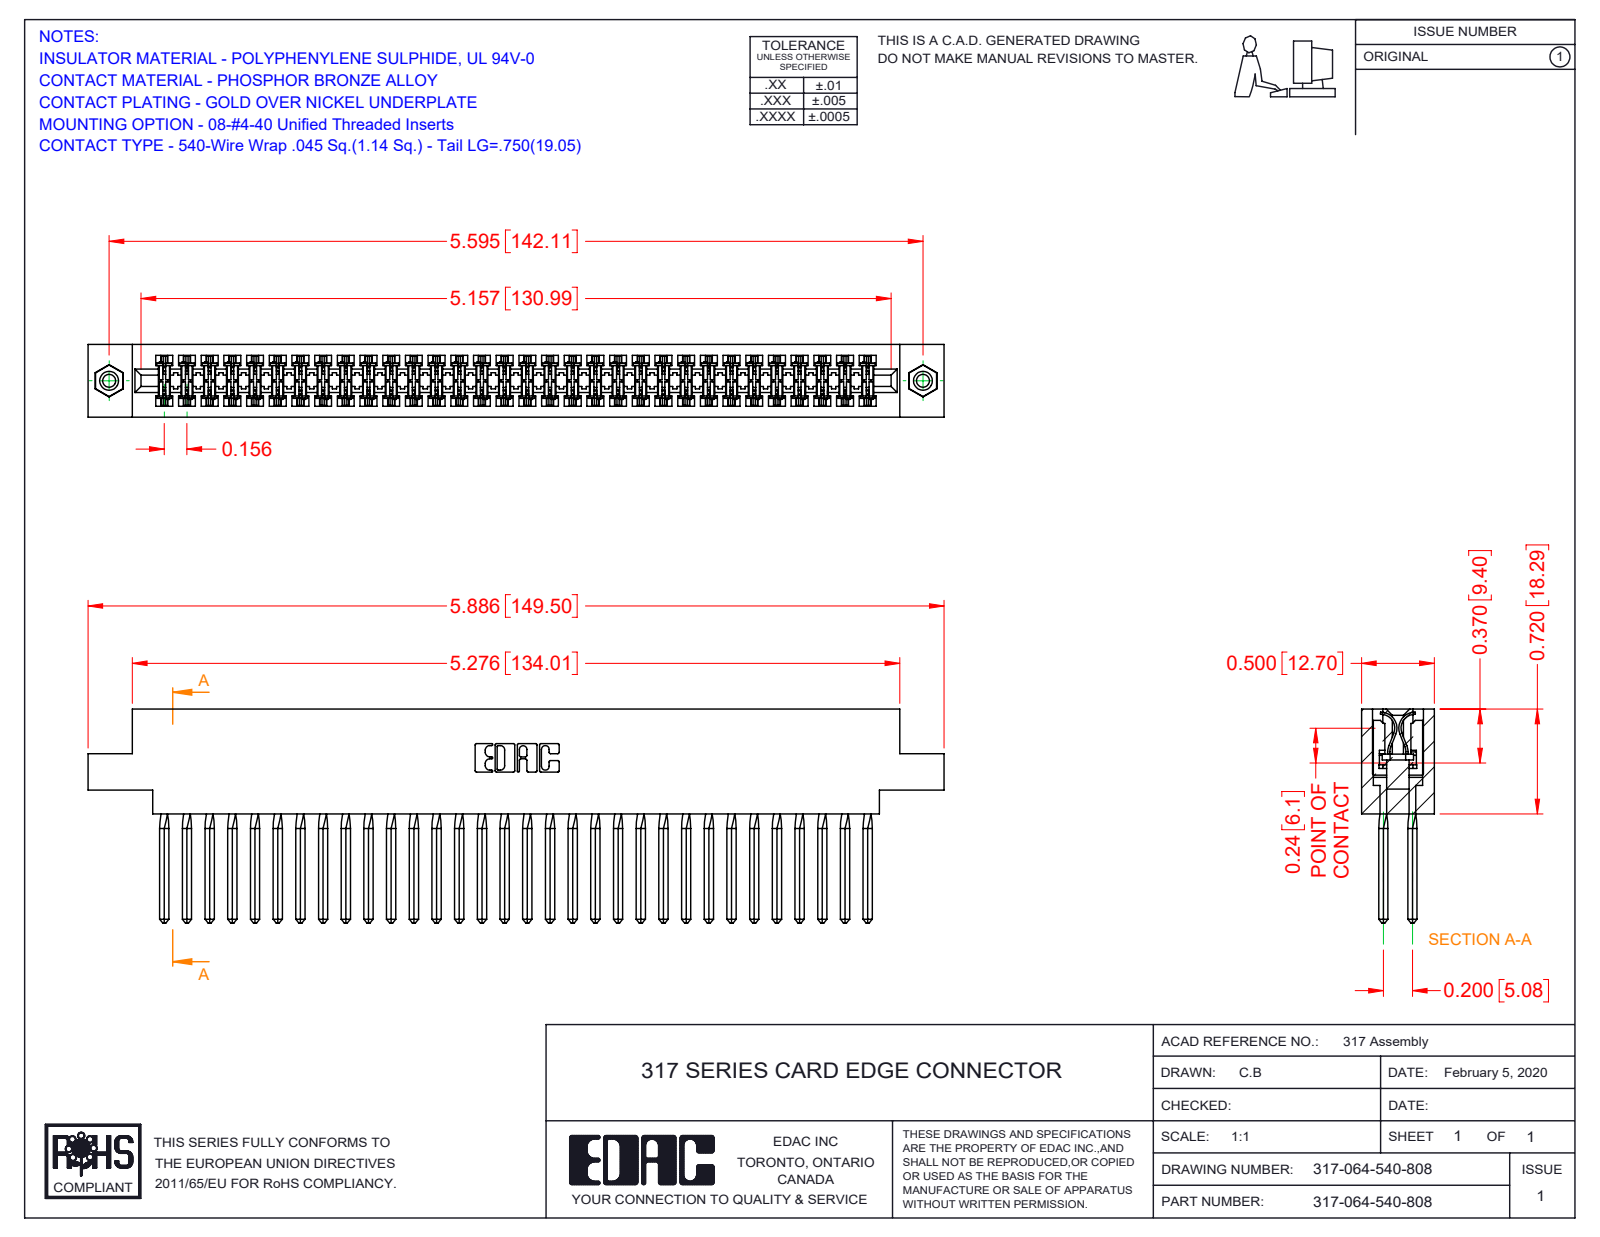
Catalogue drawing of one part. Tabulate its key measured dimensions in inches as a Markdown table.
| quantity | value |
| --- | --- |
| part name | 317-064-540-808; 317 Part_.156 Dia - TI; 317-290-001_540; 345-250-001_345-250-003-102 |
| STEP written by | SolidWorks 2016 (CONFIG_CONTROL_DESIGN) |
| units | inches |
| bodies | 67 solids, 5858 faces (4762 planar, 824 cylindrical, 272 other) |
| overall size | 5.886 × 1.47 × 0.5 |
| volume | 1.51 in³ |
| surface area | 56.64 in² |
| round holes (diameter × count) | 0.089 × 2, 0.125 × 2, 0.156 × 2 |
| round bosses / shafts (diameter × count) | 0.155 × 2 |
| partial cylindrical surfaces (radius × count) | 0.015 × 128, 0.01 × 22, 0.007 × 6, 0.031 × 6, 0.026 × 3, 0.095 × 2, 0.1 × 2, 0.11 × 2 |
| main face-to-face distances | 0.5, 0.075, 0.425, 0.35, 0.11, 0.195, 0.094, 0.2, 0.115, 0.131 |
| hole center spacings | 5.595 |
